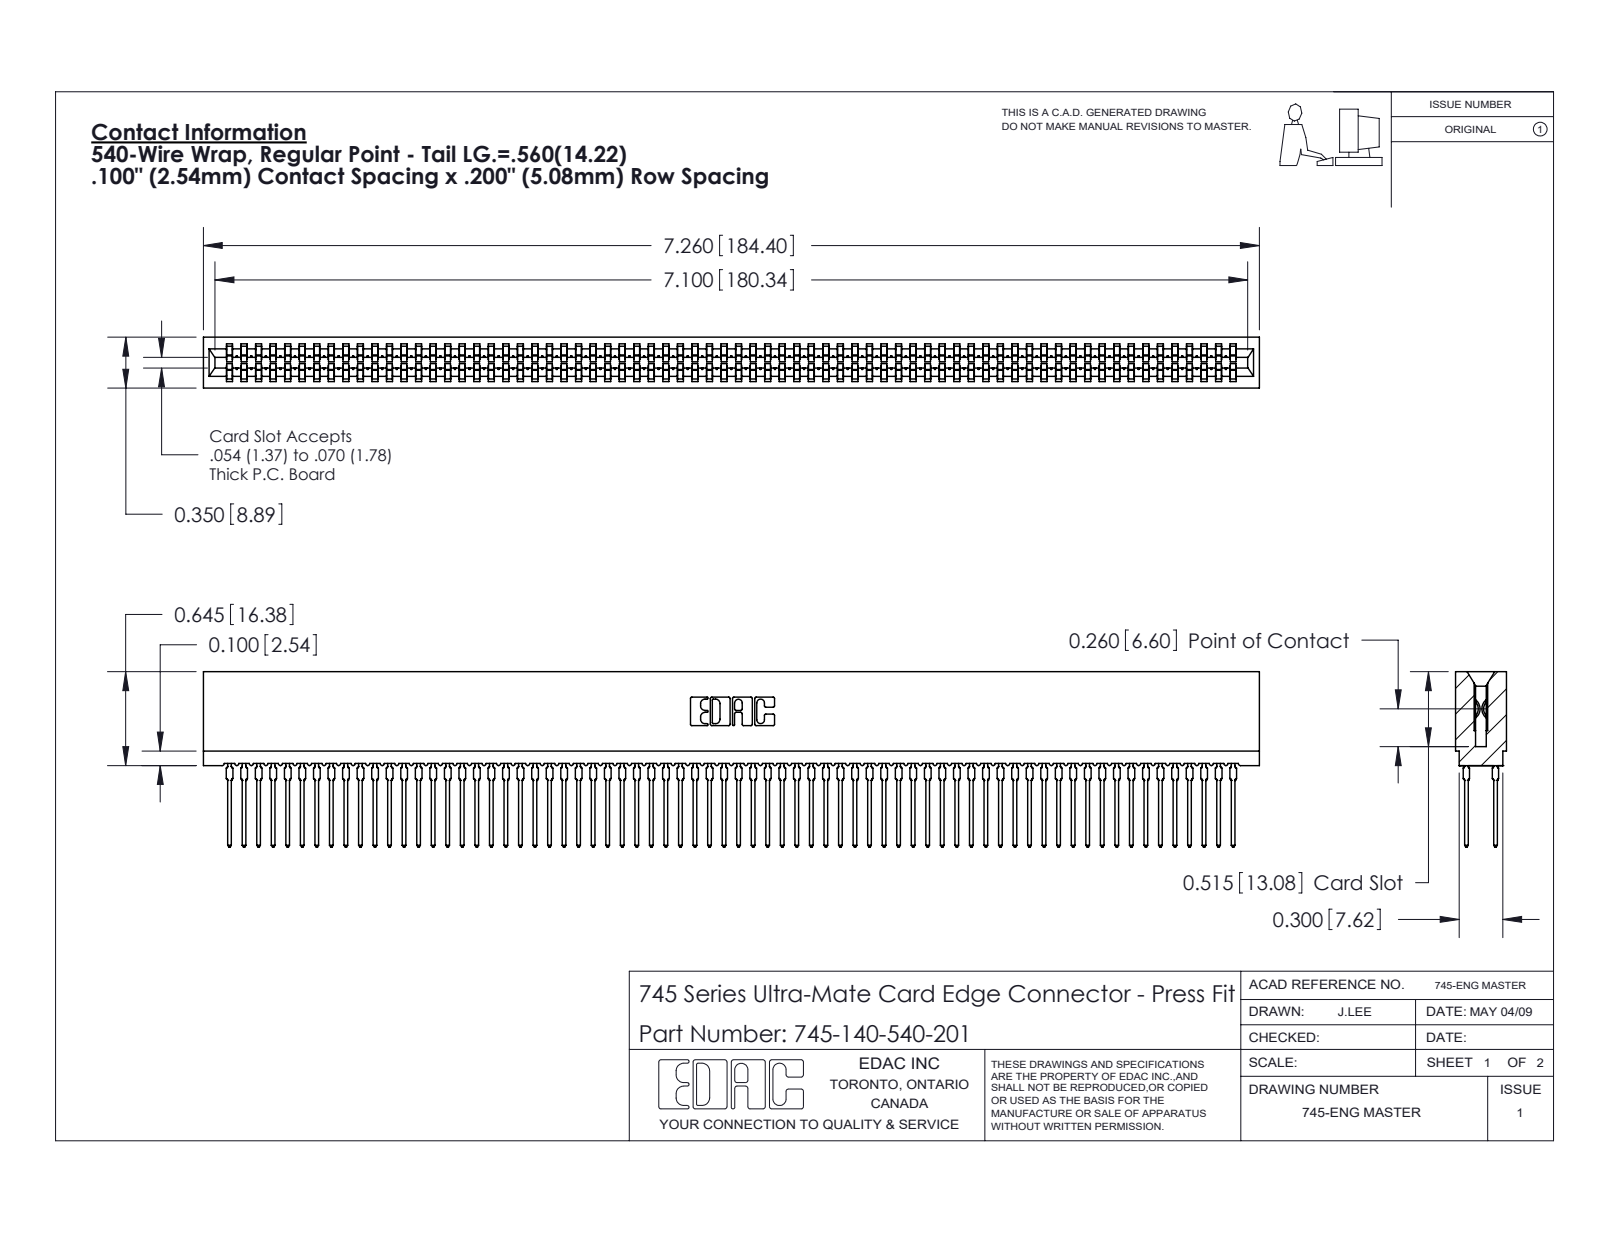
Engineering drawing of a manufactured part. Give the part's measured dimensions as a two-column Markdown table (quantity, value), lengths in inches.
| quantity | value |
| --- | --- |
| part name | 745 Part_Insulator Option - 01; 745-140-540-201; 745-292-001_540 |
| STEP written by | SolidWorks 2020 (CONFIG_CONTROL_DESIGN) |
| units | inches |
| bodies | 141 solids, 12625 faces (6495 planar, 2490 cylindrical, 3640 other) |
| overall size | 7.26 × 1.206 × 0.35 |
| volume | 1.028 in³ |
| surface area | 56.61 in² |
| partial cylindrical surfaces (radius × count) | 0.021 × 280, 0.015 × 140, 0.01 × 22, 0.005 × 8, 0.011 × 8, 0.007 × 6, 0.031 × 6, 0.026 × 3 |
| main face-to-face distances | 0.063, 0.287, 0.35, 0.2, 0.045, 0.305, 0.018, 0.243, 0.138, 0.212 |
